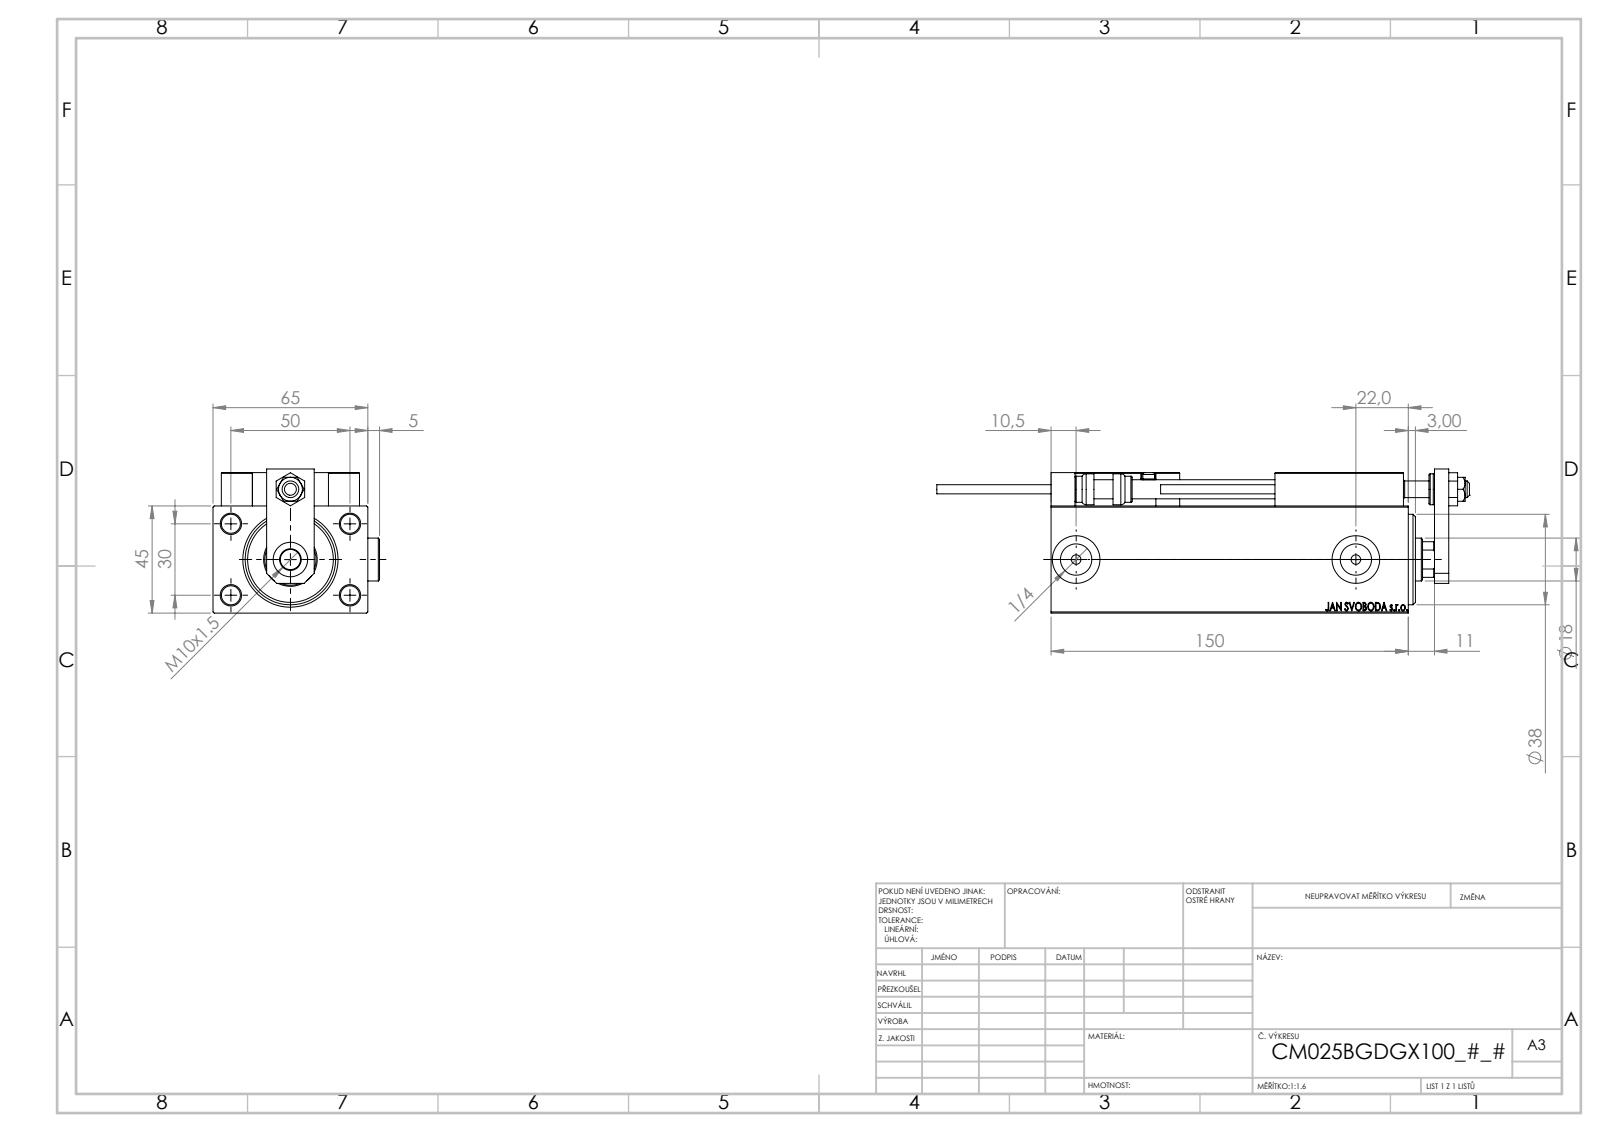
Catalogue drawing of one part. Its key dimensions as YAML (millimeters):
part_name: "SWITCH_X_FRONT_BACK; ZARAZKA; SWITCH X; SWITCH DIM B,W (+8 more)"
step_written_by: "SolidWorks 2019 (CONFIG_CONTROL_DESIGN)"
units: millimeters
bodies: {solids: 26, faces: 1372, planar: 595, cylindrical: 200, other: 577}
overall_size: [223.7, 69.9, 60.5]
volume: 456567
surface_area: 97544
round_holes:
  - {diameter: 8, count: 9}
  - {diameter: 4, count: 6}
  - {diameter: 3.2, count: 4}
  - {diameter: 5, count: 2}
  - {diameter: 13.16, count: 2}
  - {diameter: 20, count: 2}
  - {diameter: 7, count: 1}
  - {diameter: 8.5, count: 1}
  - {diameter: 14.5, count: 1}
  - {diameter: 18, count: 1}
  - {diameter: 21.5, count: 1}
  - {diameter: 22.5, count: 1}
round_bosses_or_shafts:
  - {diameter: 18, count: 2}
  - {diameter: 5, count: 2}
  - {diameter: 3.8, count: 2}
  - {diameter: 13, count: 1}
  - {diameter: 11, count: 1}
partial_cylinders:
  - {radius: 0.3, count: 30}
  - {radius: 3, count: 2}
  - {radius: 8.5, count: 1}
face_to_face_distances: [45, 65, 14, 6, 59, 5, 13, 3.5, 161, 19]
hole_center_spacings: [29.15, 11.37, 20, 28.9, 29.59, 29.69, 30, 36.06]
